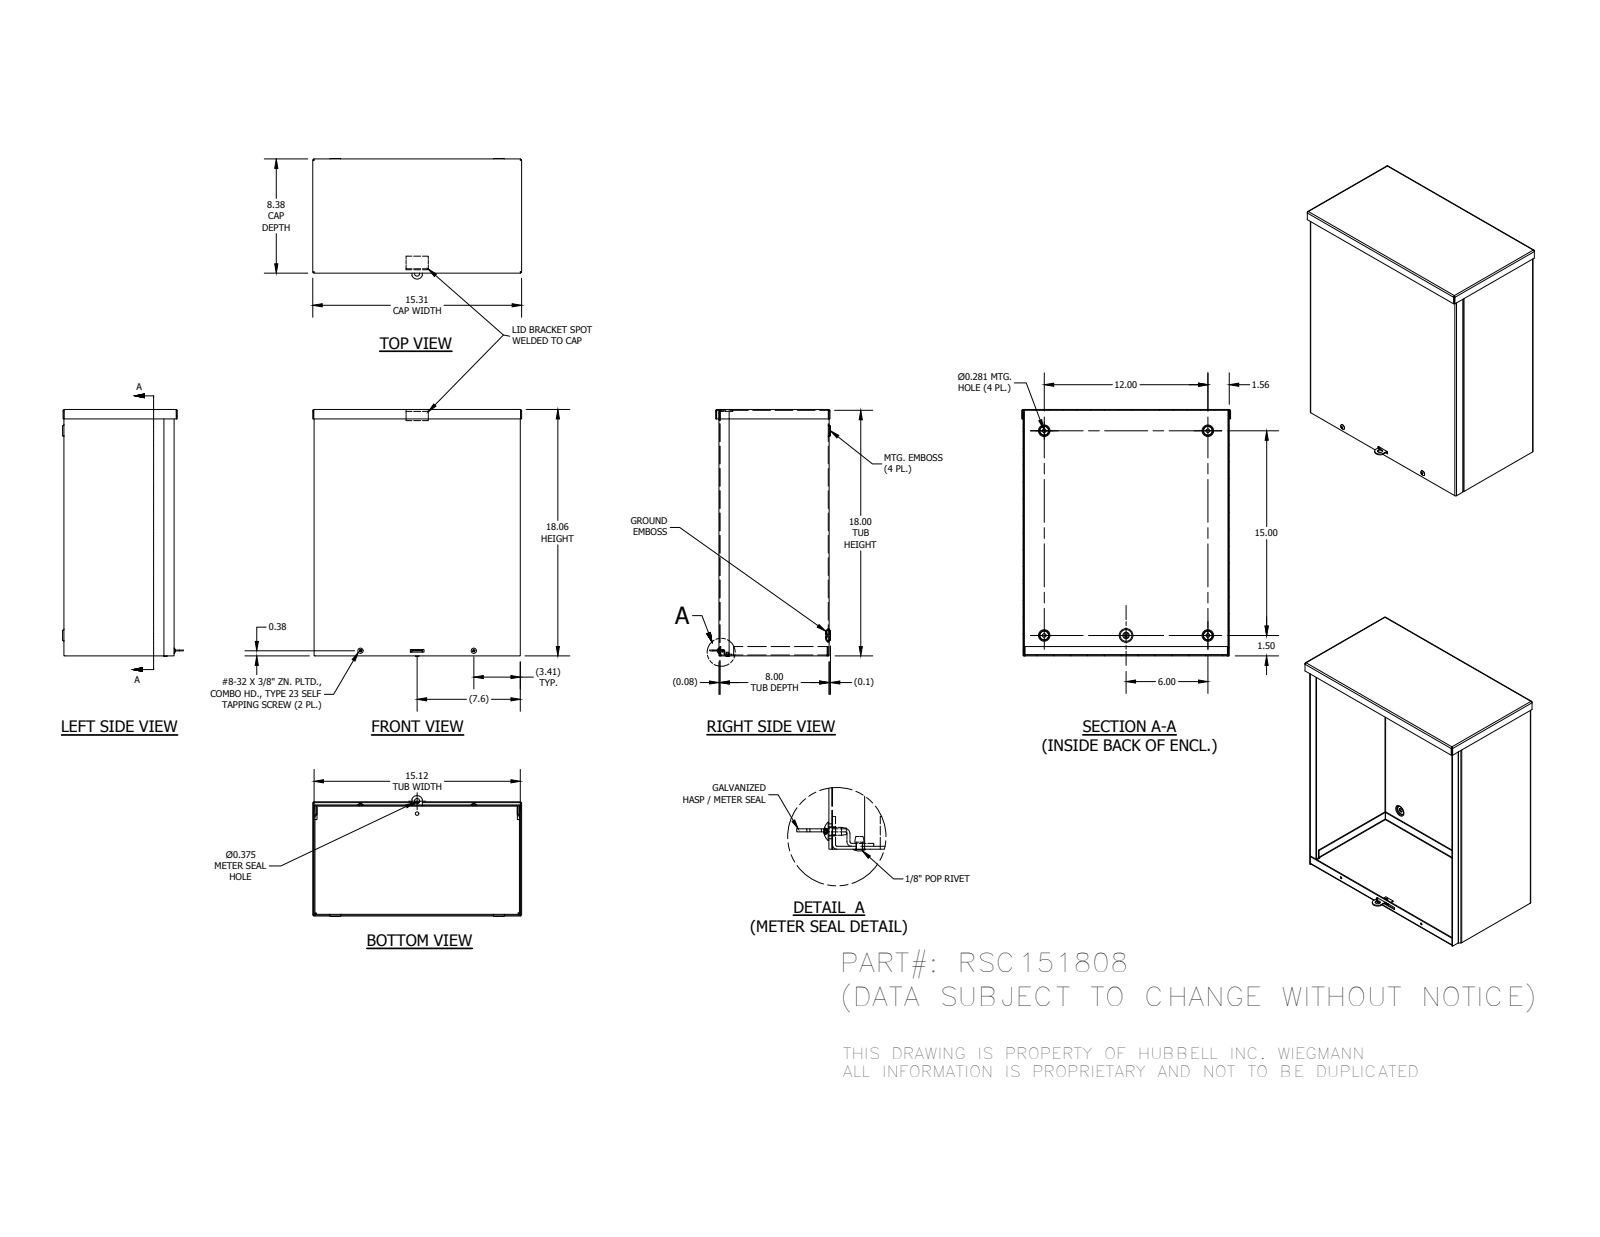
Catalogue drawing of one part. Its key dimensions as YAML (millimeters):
part_name: "RSC151808BKPA; RSC1508EWPA; RSC1518LFA; RSC1508CPA (+5 more)"
step_written_by: "Autodesk Inventor 2014 (AUTOMOTIVE_DESIGN)"
units: millimeters
bodies: {solids: 9, faces: 320, planar: 183, cylindrical: 61, other: 76}
overall_size: [459.79, 388.91, 224.8]
volume: 1179000
surface_area: 1509000
round_holes:
  - {diameter: 7.14, count: 4}
  - {diameter: 7.94, count: 4}
  - {diameter: 3.73, count: 2}
  - {diameter: 3.17, count: 1}
  - {diameter: 3.45, count: 1}
  - {diameter: 4.34, count: 1}
  - {diameter: 9.52, count: 1}
round_bosses_or_shafts:
  - {diameter: 9.75, count: 2}
  - {diameter: 4.17, count: 2}
  - {diameter: 6.65, count: 1}
  - {diameter: 5.93, count: 1}
  - {diameter: 3.17, count: 1}
partial_cylinders:
  - {radius: 0.79, count: 19}
  - {radius: 2.37, count: 18}
  - {radius: 2.67, count: 1}
  - {radius: 10.16, count: 1}
face_to_face_distances: [1.57, 203.6, 382.57, 205.17, 202.03, 457.2, 381, 384.14, 458.77, 455.63]
hole_center_spacings: [54.86, 259.55, 109.37, 211.14, 412.25, 484.05, 152.4, 304.8]
